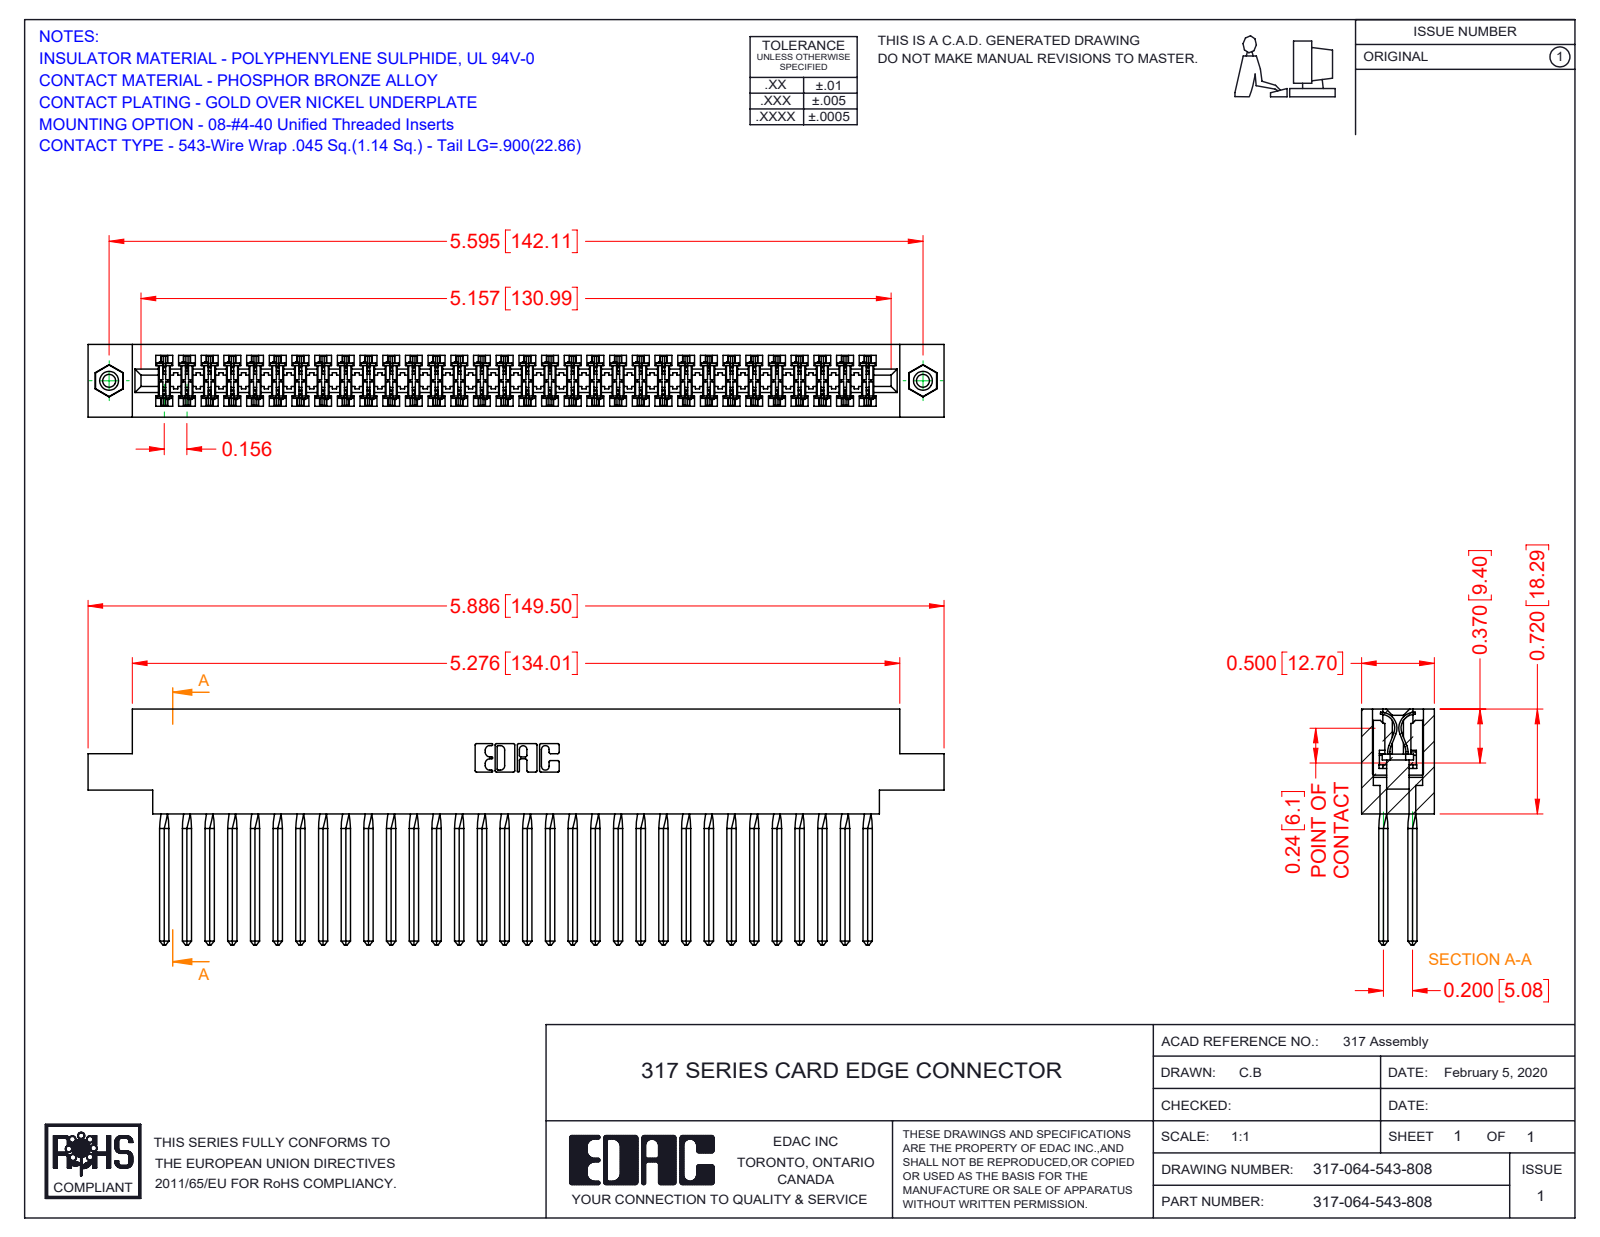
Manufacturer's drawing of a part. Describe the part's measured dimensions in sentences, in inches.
The part is named "345-250-001_345-250-003-102; 317-290-001_543; 317 Part_.156 Dia - TI; 317-064-543-808". Its 3-D file was written by "SolidWorks 2016 (CONFIG_CONTROL_DESIGN)". It is 67 solids with 5858 faces: 4762 planar, 824 cylindrical and 272 other. Overall it measures 5.886 by 1.62 by 0.5 inches. Its volume is 1.53 cubic inches and its surface area 58.36 square inches. Round holes: 2 of diameter 0.089, 2 of diameter 0.125, 2 of diameter 0.156. Round bosses or shafts: 2 of diameter 0.155. Partial cylindrical surfaces (rounded edges, fillets, slot ends): 128 of radius 0.015, 22 of radius 0.01, 6 of radius 0.007, 6 of radius 0.031, 3 of radius 0.026, 2 of radius 0.095, 2 of radius 0.1, 2 of radius 0.11. The main face-to-face distances are 0.5, 0.075, 0.425, 0.35, 0.11, 0.195, 0.094, 0.2, 0.115, 0.131. The hole center spacings are 5.595.
